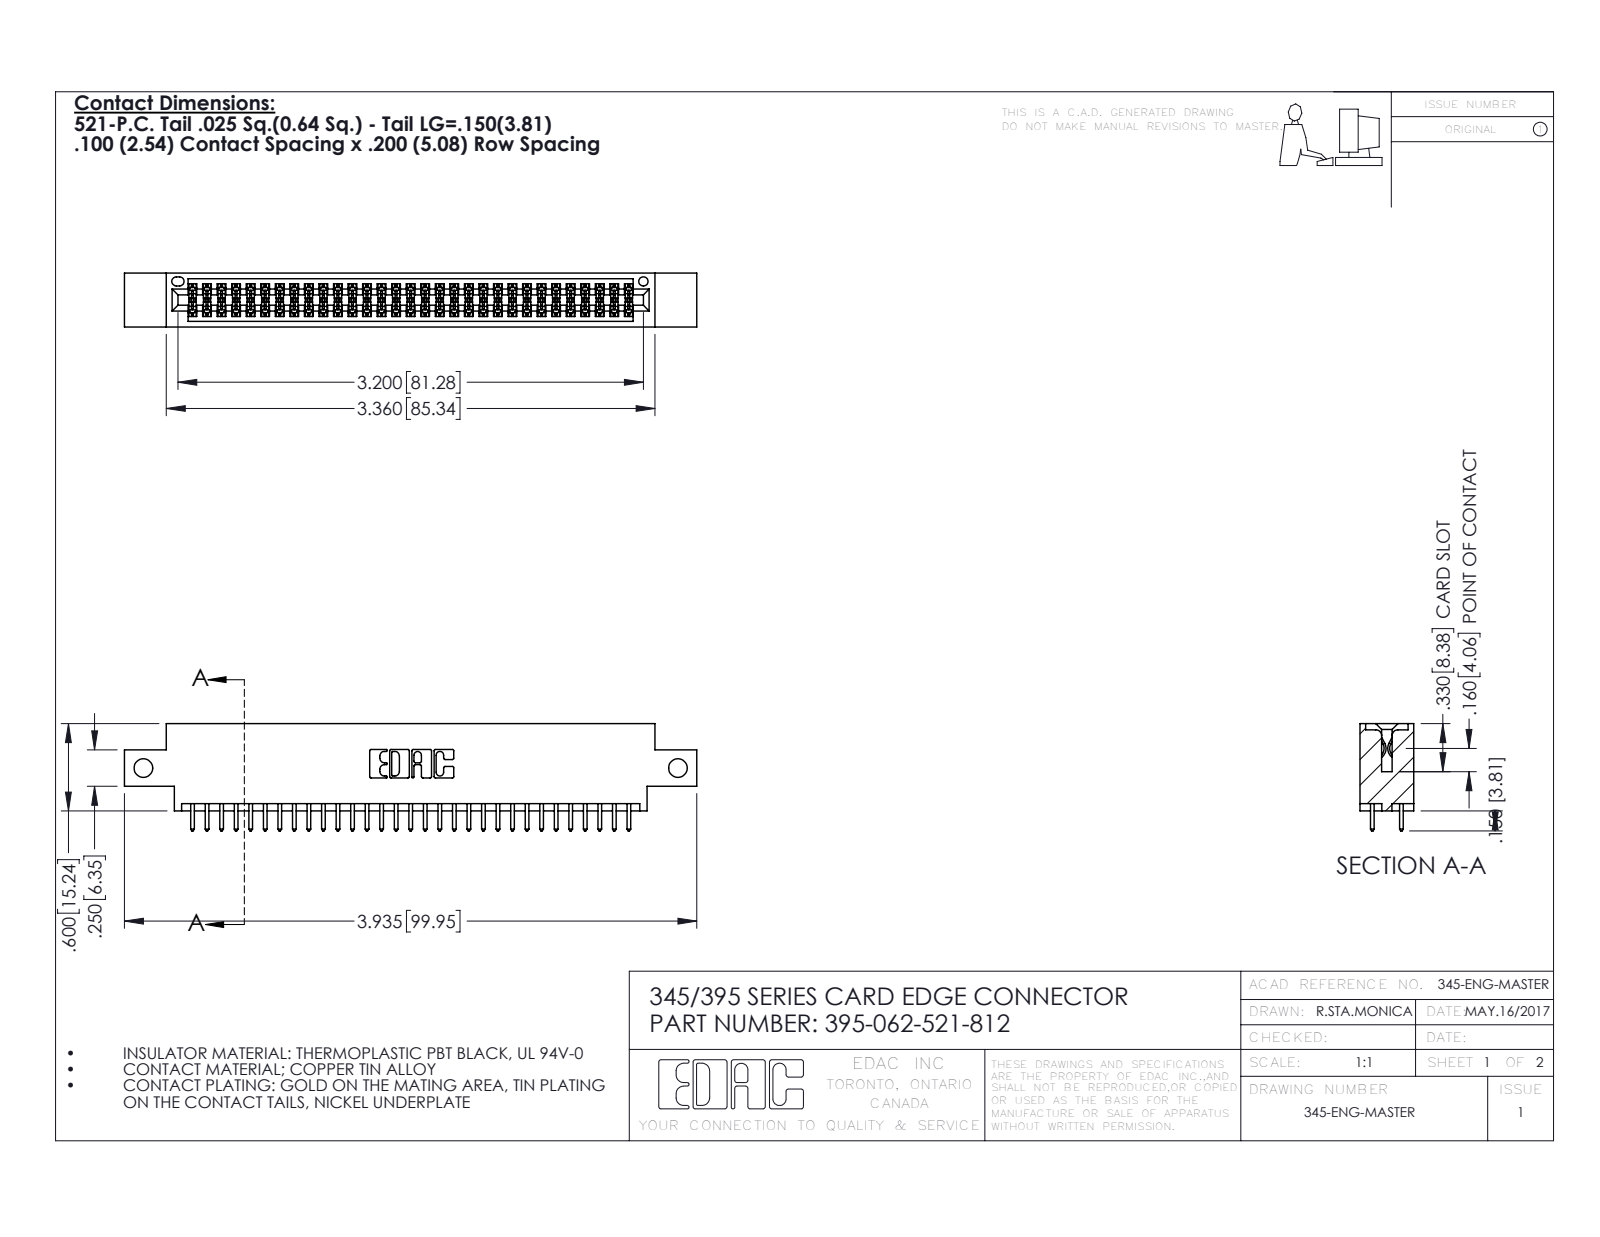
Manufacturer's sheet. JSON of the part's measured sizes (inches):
{"part_name": "345 Part_0.170 Offset - Side Mount; 395-062-521-812; 345-292-001_345-293-121", "step_written_by": "SolidWorks 2016 (CONFIG_CONTROL_DESIGN)", "units": "inches", "bodies": {"solids": 63, "faces": 3230, "planar": 2130, "cylindrical": 1100, "other": 0}, "overall_size": [3.935, 0.737, 0.37], "volume_in3": 0.572, "surface_area_in2": 20.92, "round_holes": [[0.128, 2], [0.064, 1]], "partial_cylinders_radius": [[0.006, 93], [0.01, 62], [0.01, 22], [0.007, 6], [0.031, 6], [0.026, 3], [0.014, 2], [0.019, 2]], "face_to_face_distances": [0.298, 0.072, 0.37, 0.2, 0.098, 0.272, 0.025, 0.225, 0.175, 0.149], "hole_center_spacings": [3.675]}
